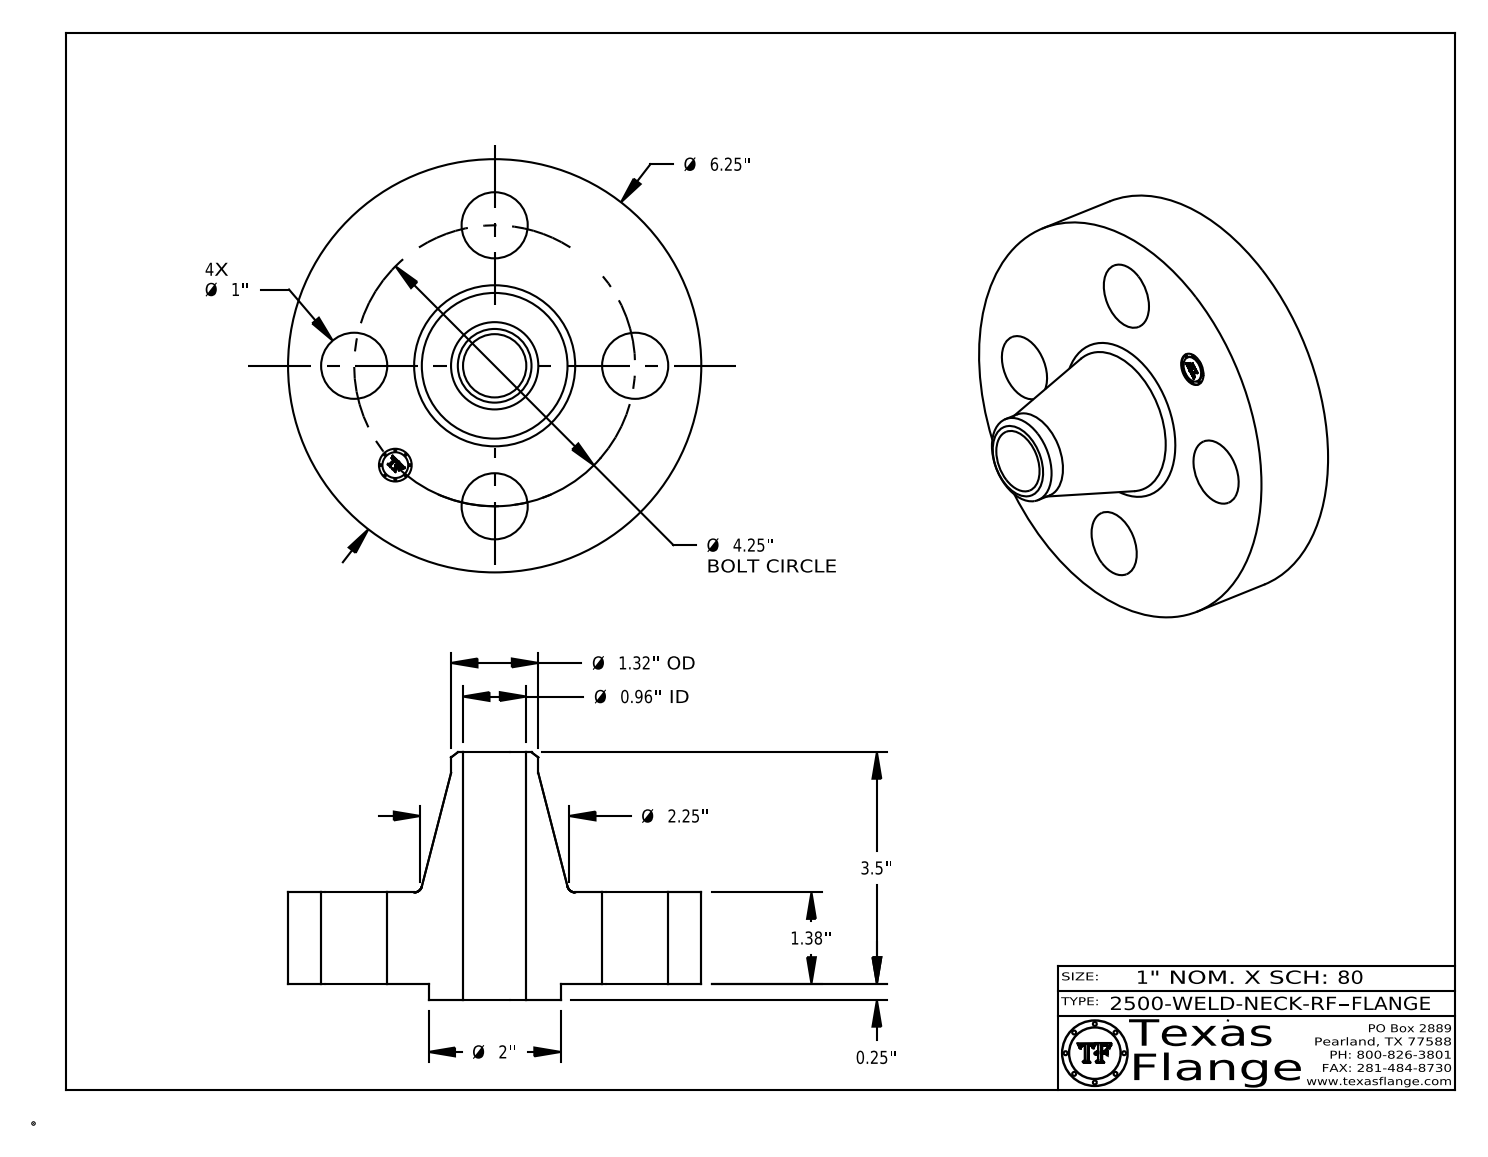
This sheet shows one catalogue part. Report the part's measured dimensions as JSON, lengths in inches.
{"part_name": "2500-WELD-NECK-RF", "step_written_by": "CATIA V5 STEP AP214 (AUTOMOTIVE_DESIGN)", "units": "inches", "bodies": {"solids": 1, "faces": 411, "planar": 369, "cylindrical": 36, "other": 6}, "overall_size": [6.25, 6.25, 3.75], "volume_in3": 41.14, "surface_area_in2": 119.7, "round_holes": [[1, 4], [0.495, 1], [0.957, 1]], "round_bosses_or_shafts": [[0.03, 8], [6.25, 1], [2, 1], [1.32, 1], [0.39, 1]], "face_to_face_distances": [1.38, 0.25, 1.63, 3.75, 3.5, 2.12, 1.615, 1.365, 0.015, 2.135], "hole_center_spacings": [2.125, 3.006, 1.626, 3.927, 4.25]}
